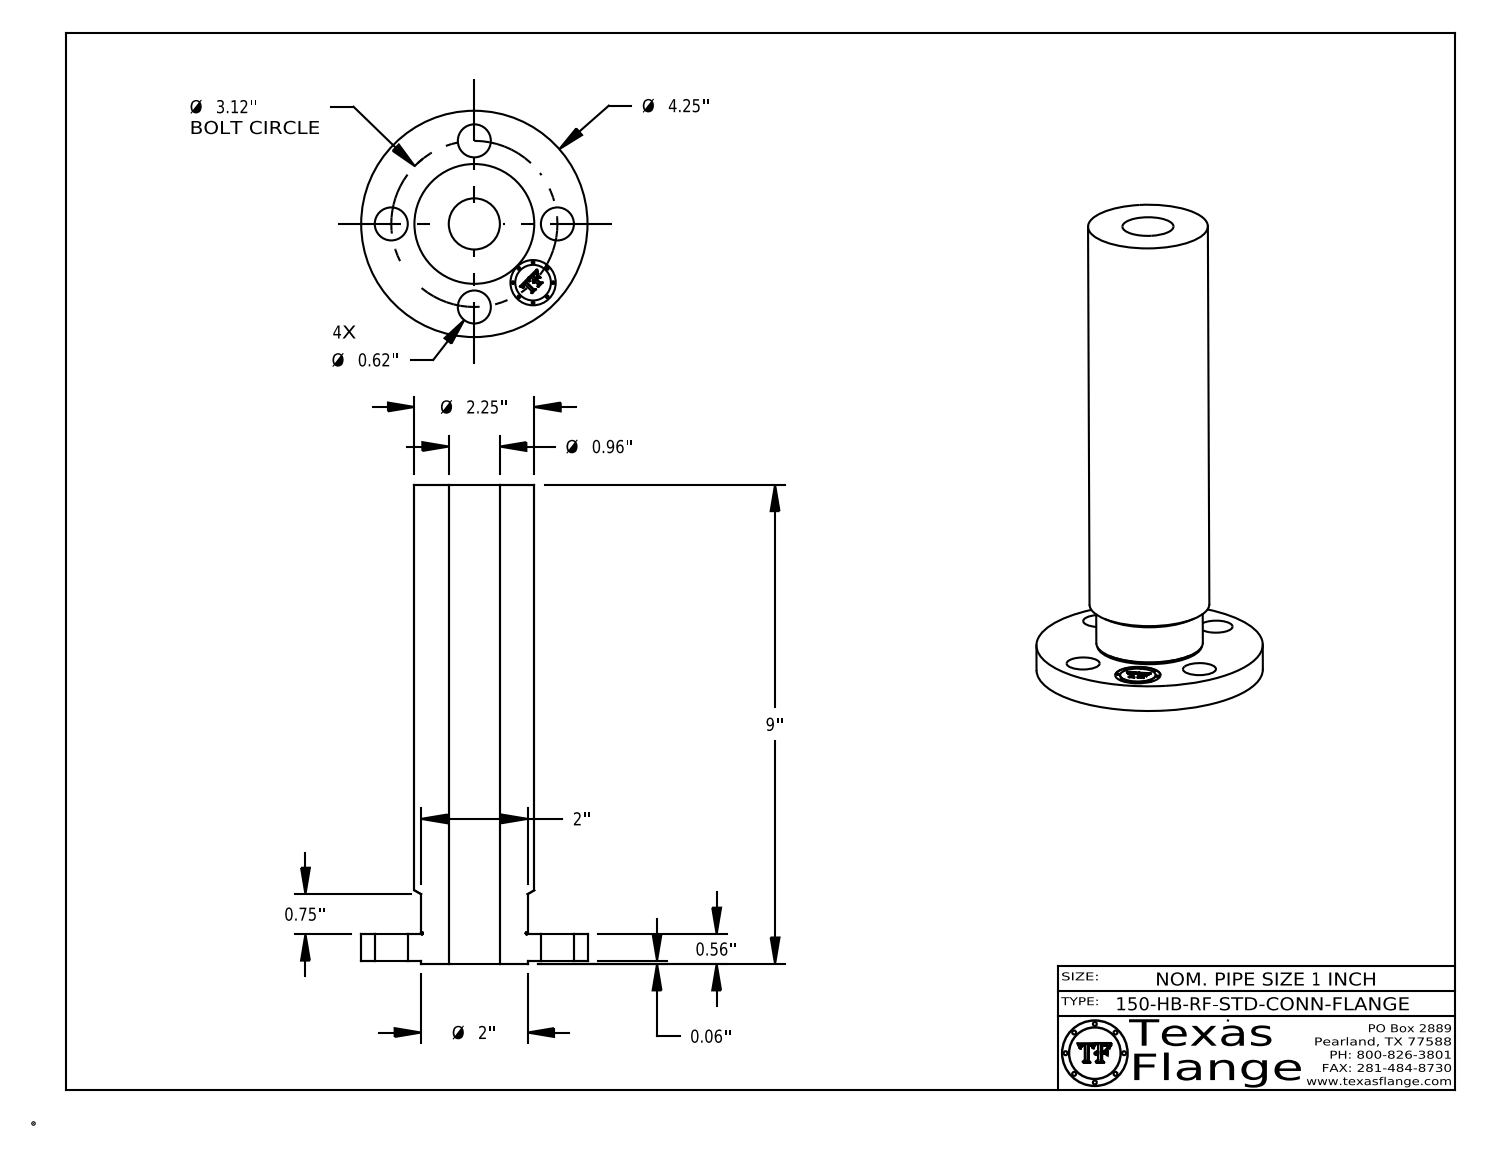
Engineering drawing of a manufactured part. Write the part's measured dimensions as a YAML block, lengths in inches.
part_name: "1-150-HB-RF-STD-CONN-FLANGE"
step_written_by: "CATIA V5 STEP AP214 (AUTOMOTIVE_DESIGN)"
units: inches
bodies: {solids: 1, faces: 413, planar: 369, cylindrical: 38, other: 6}
overall_size: [9, 4.25, 4.25]
volume: 33.03
surface_area: 123.2
round_holes:
  - {diameter: 0.62, count: 4}
  - {diameter: 0.85, count: 1}
  - {diameter: 0.96, count: 1}
round_bosses_or_shafts:
  - {diameter: 0.051, count: 8}
  - {diameter: 4.25, count: 1}
  - {diameter: 2.25, count: 1}
  - {diameter: 2, count: 1}
  - {diameter: 0.67, count: 1}
face_to_face_distances: [0.498, 8.937, 8.44, 0.063, 0.56, 9, 0.555, 0.493, 8.445, 0.254]
hole_center_spacings: [1.56, 2.206, 1.194, 2.882, 3.12, 1.56]
